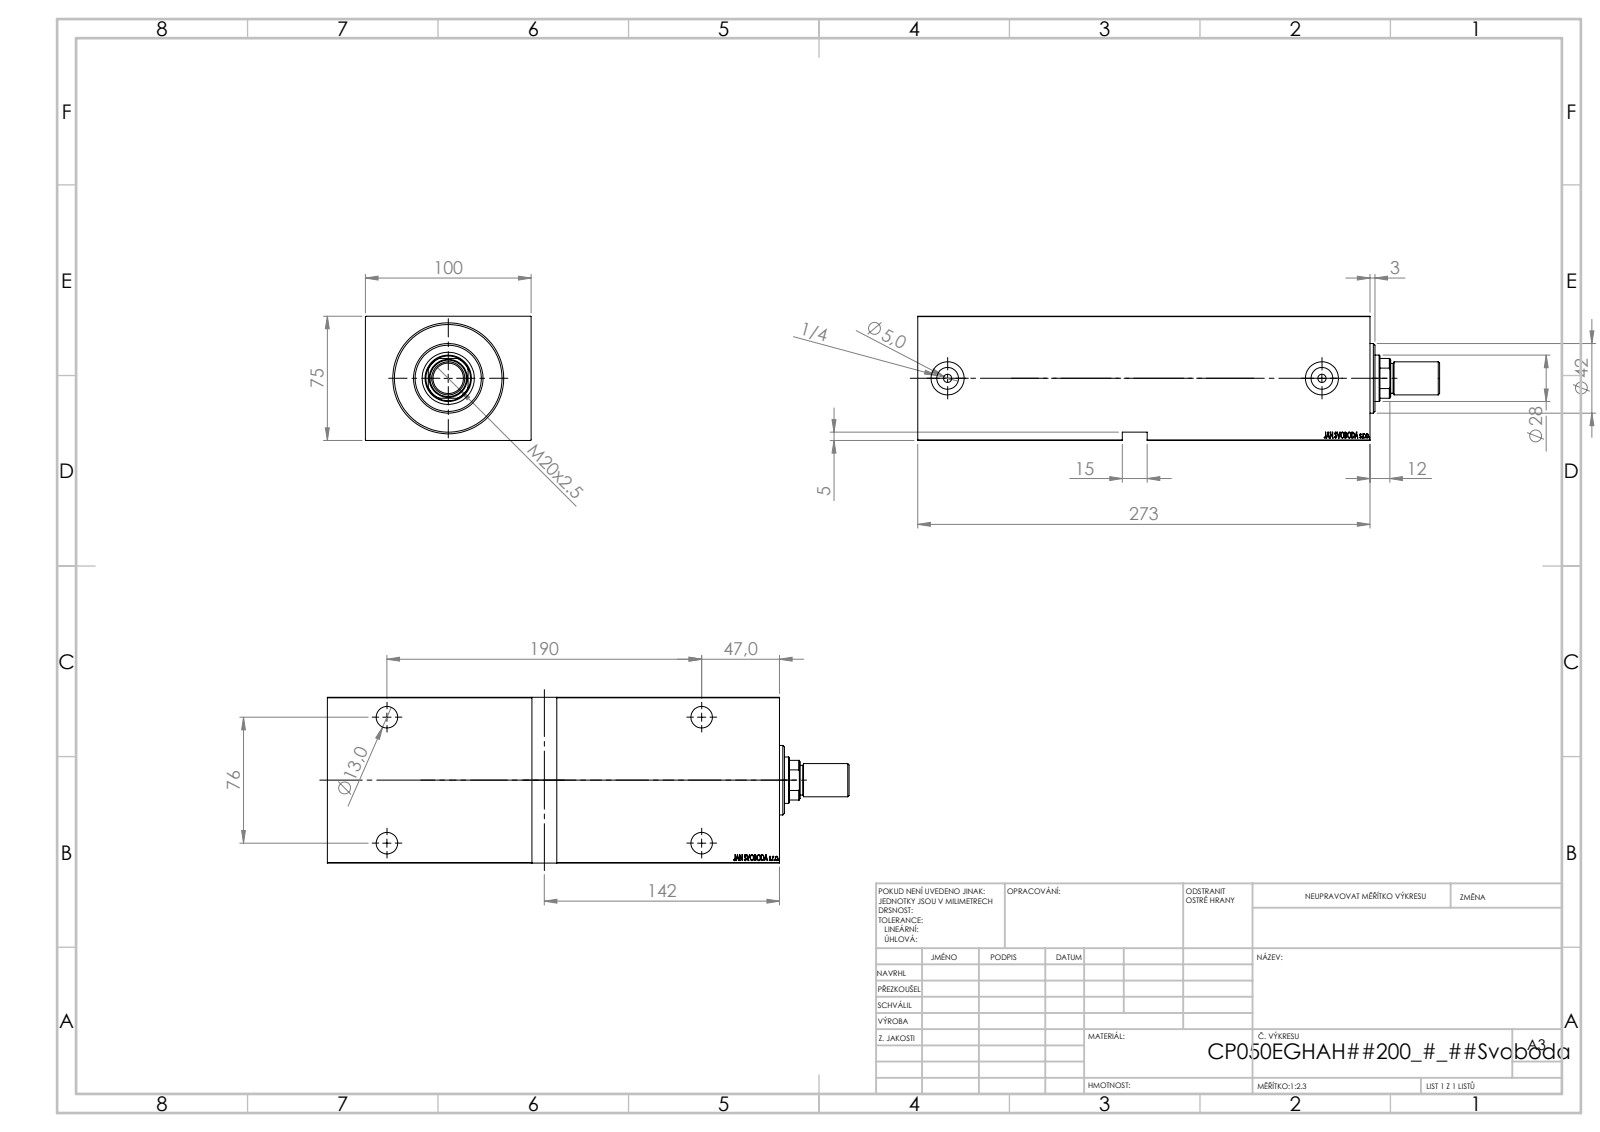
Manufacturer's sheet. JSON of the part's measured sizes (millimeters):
{"part_name": "V450CM_E_VCP; V450CM_E_Body; V450CM_MALE_METRIC; V450CM_VC_B", "step_written_by": "SolidWorks 2019 (CONFIG_CONTROL_DESIGN)", "units": "millimeters", "bodies": {"solids": 4, "faces": 870, "planar": 414, "cylindrical": 56, "other": 400}, "overall_size": [315, 100, 75], "volume_mm3": 1732000, "surface_area_mm2": 211981, "round_holes": [[13, 4], [19, 4], [5, 2], [13.16, 2], [20, 2], [18.5, 1], [28, 1], [31.5, 1], [50, 1], [65, 1]], "round_bosses_or_shafts": [[52, 1], [42, 1], [20, 1], [18, 1]], "partial_cylinders_radius": [[13.5, 1]], "face_to_face_distances": [75, 100, 273, 5, 14, 259, 254, 268, 47, 256.4], "hole_center_spacings": [76, 190, 204.64, 226]}
